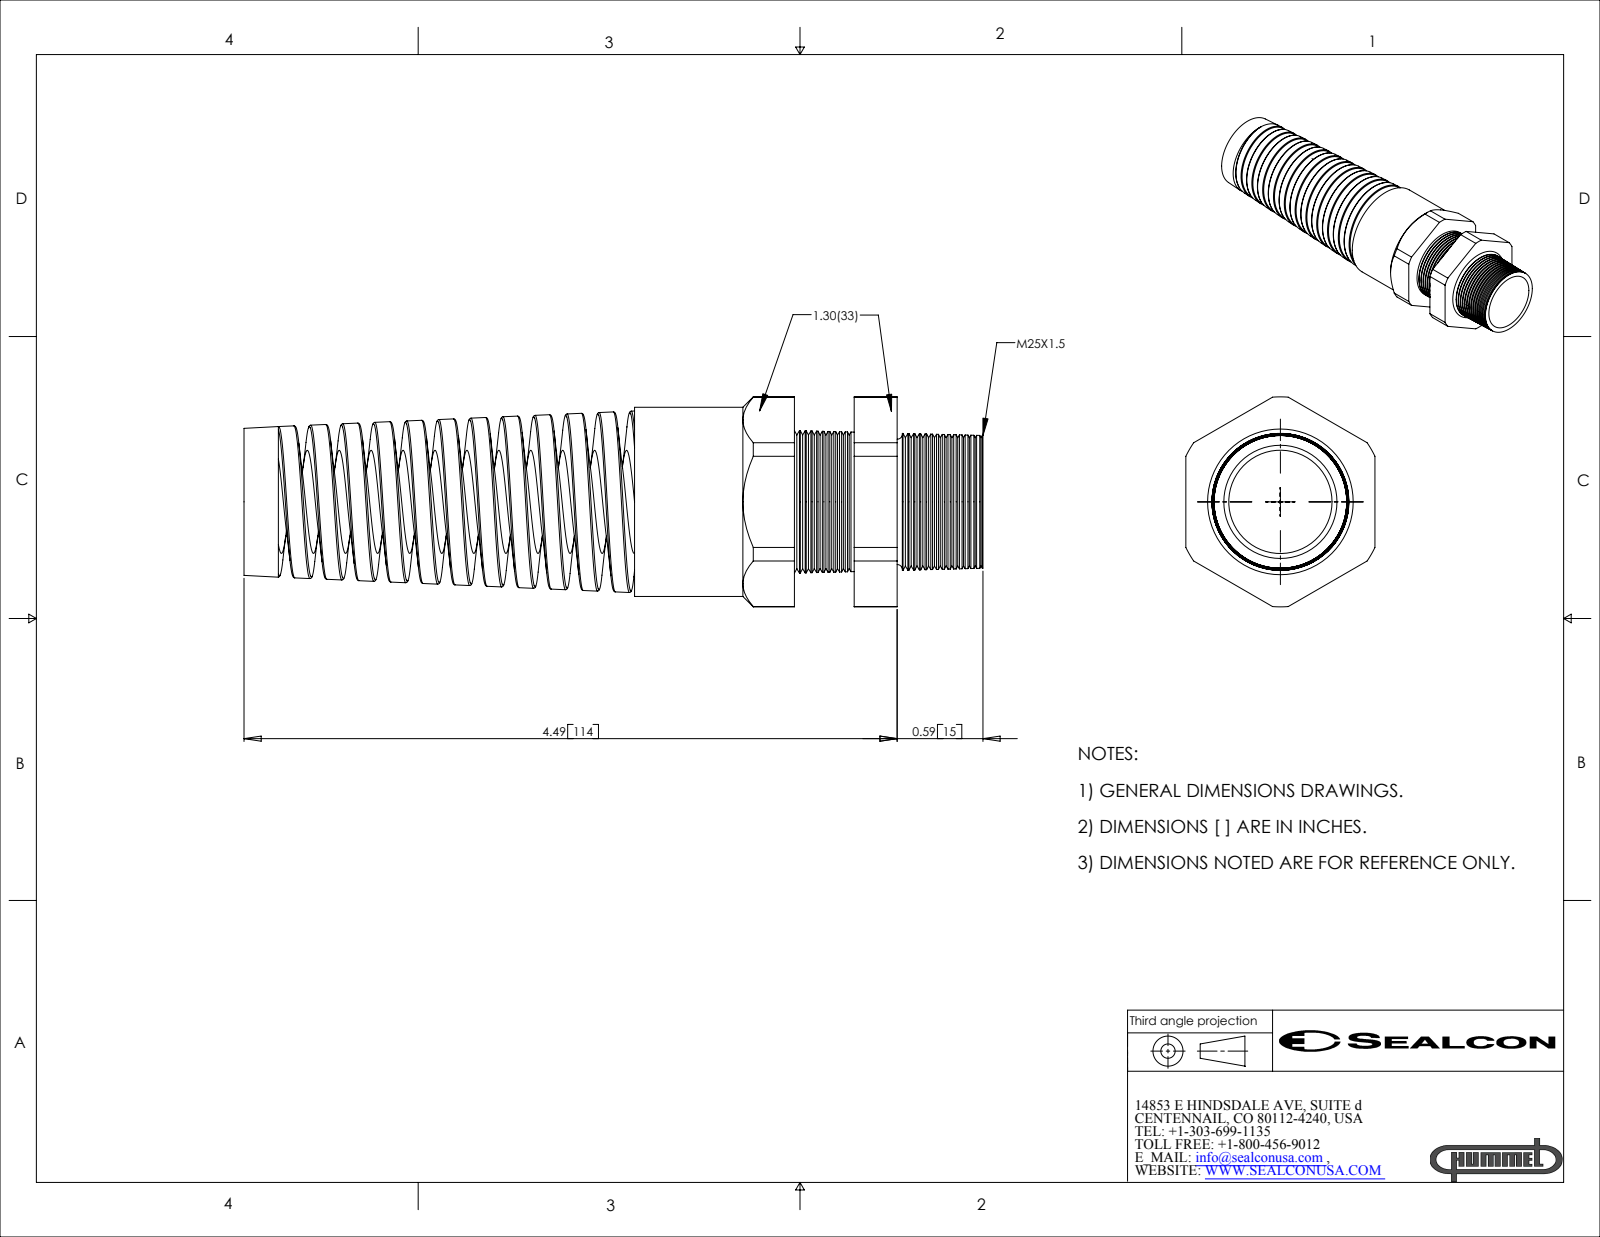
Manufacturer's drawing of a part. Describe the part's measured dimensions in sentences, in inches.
The part is named "CF25DA-BK". Its 3-D file was written by "SolidWorks 2007 (CONFIG_CONTROL_DESIGN)". It is 2 solids with 264 faces: 25 planar, 47 cylindrical and 192 other. Overall it measures 5.08 by 1.443 by 1.3 inches. Its volume is 2.68 cubic inches and its surface area 45.07 square inches. Round holes: 1 of diameter 0.71, 1 of diameter 0.735. Round bosses or shafts: 1 of diameter 1.3, 1 of diameter 0.949. Partial cylindrical surfaces (rounded edges, fillets, slot ends): 1 of radius 0.721. The main face-to-face distances are 1.3, 0.411, 0.706, 0.295, 1.099, 1.51, 1.806, 2.685, 3.784, 4.195.
